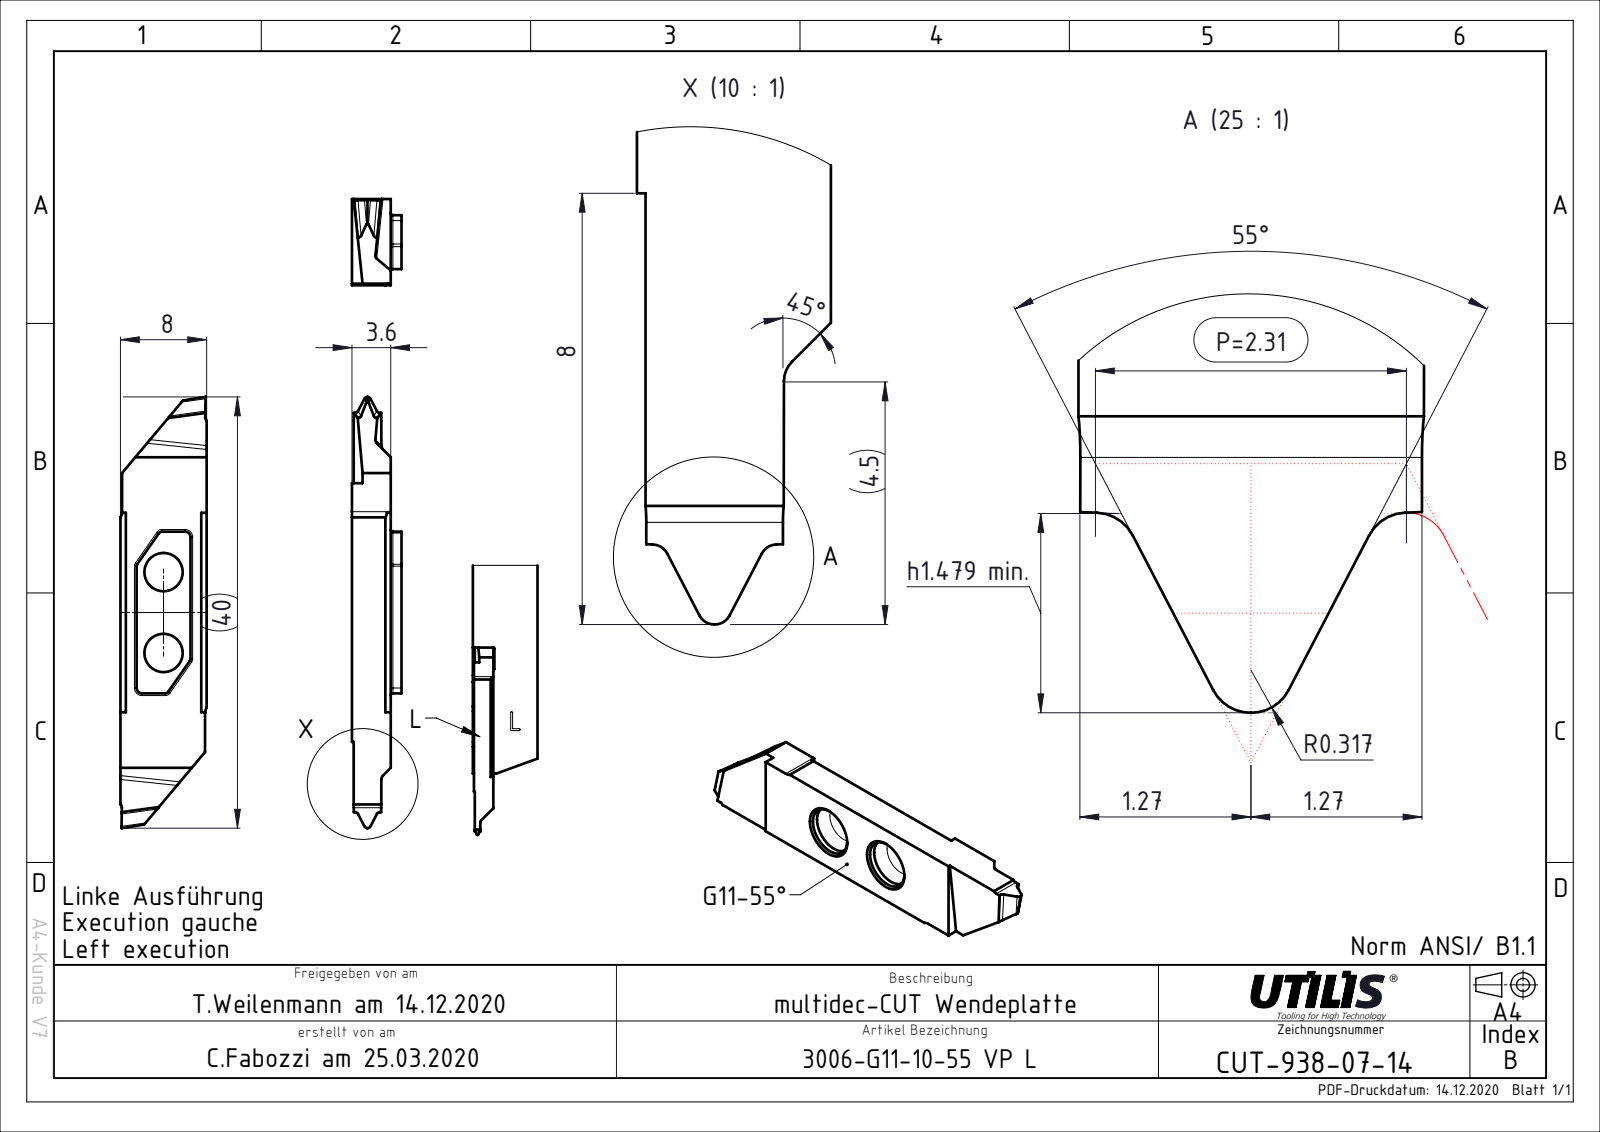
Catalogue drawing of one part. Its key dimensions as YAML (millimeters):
part_name: "CUT-938-07; ASME Y14.5"
step_written_by: "FormatWorks Professional (AP242_MANAGED_MODEL_BASED_3D_ENGINEERING_MIM_LF)"
units: millimeters
bodies: {solids: 1, faces: 50, planar: 32, cylindrical: 18, other: 0}
overall_size: [40, 8, 3.6]
volume: 848
surface_area: 859
round_holes:
  - {diameter: 3.55, count: 2}
partial_cylinders:
  - {radius: 0.32, count: 8}
  - {radius: 0.4, count: 2}
  - {radius: 0.5, count: 2}
  - {radius: 1, count: 2}
face_to_face_distances: [3.6, 8, 7.85, 22.54, 7.7, 4.2, 4.35, 12.05, 12.2, 115.9]
hole_center_spacings: [7.5]
